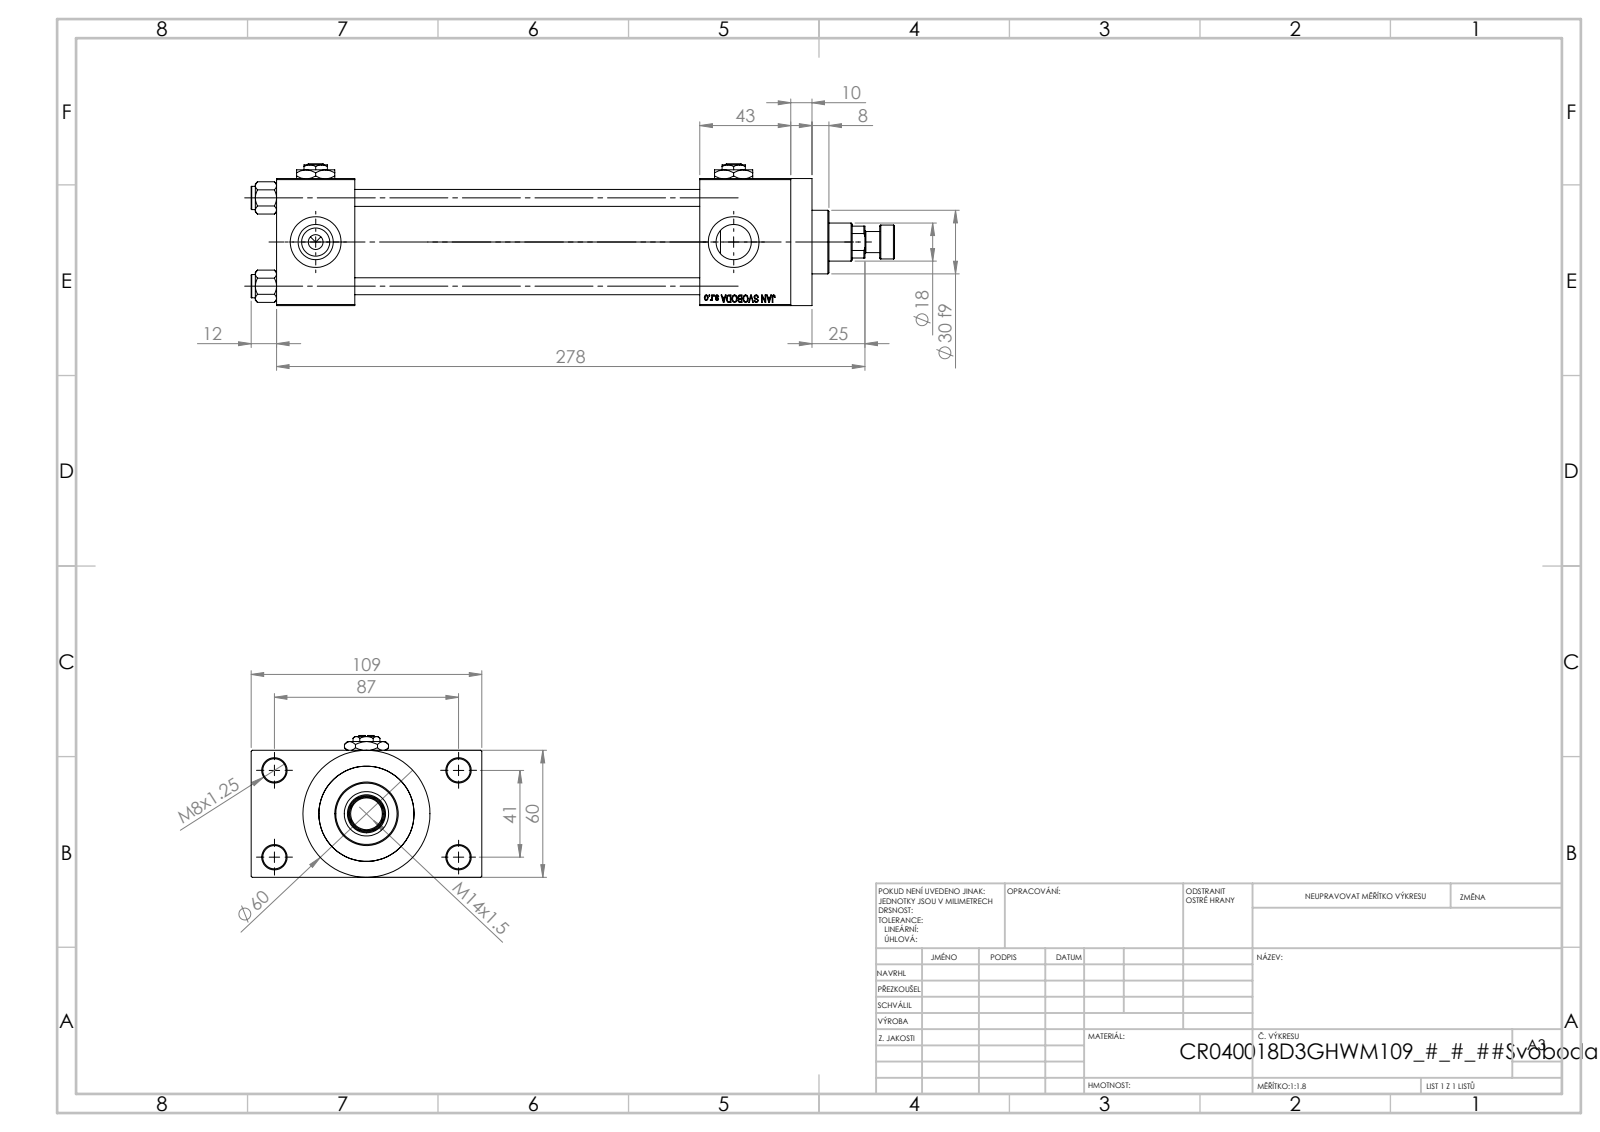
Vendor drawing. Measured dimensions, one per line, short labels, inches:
name: V215CR_D_TYCINKA; V215CR_D_Body; V215_VC_A; NUT_M5_D (+3 more)
written by: SolidWorks 2019 (CONFIG_CONTROL_DESIGN)
unit: in
bodies: 14 solids, 1218 faces (549 planar, 103 cylindrical, 566 other)
size: 11.969 × 4.291 × 2.638
volume: 36.78 in³; area: 265.1 in²
holes: 4× ⌀0.315, 4× ⌀0.433, 4× ⌀0.656, 4× ⌀0.945, 3× ⌀0.276, 1× ⌀0.335, 1× ⌀0.709, 1× ⌀0.827, 1× ⌀1.22, 1× ⌀1.575, 1× ⌀1.772
bosses: 4× ⌀0.433, 1× ⌀2.362, 1× ⌀1.811, 1× ⌀1.181, 1× ⌀0.63, 1× ⌀0.394
rounds: 1× R0.335
face distances: 2.362, 0.965, 6.417, 3.327, 1.457, 7.874, 1.693, 9.567, 8.11, 0.394
hole spacings: 0.892, 1.161, 1.642, 1.856, 1.893, 2.533, 3.011, 1.614
